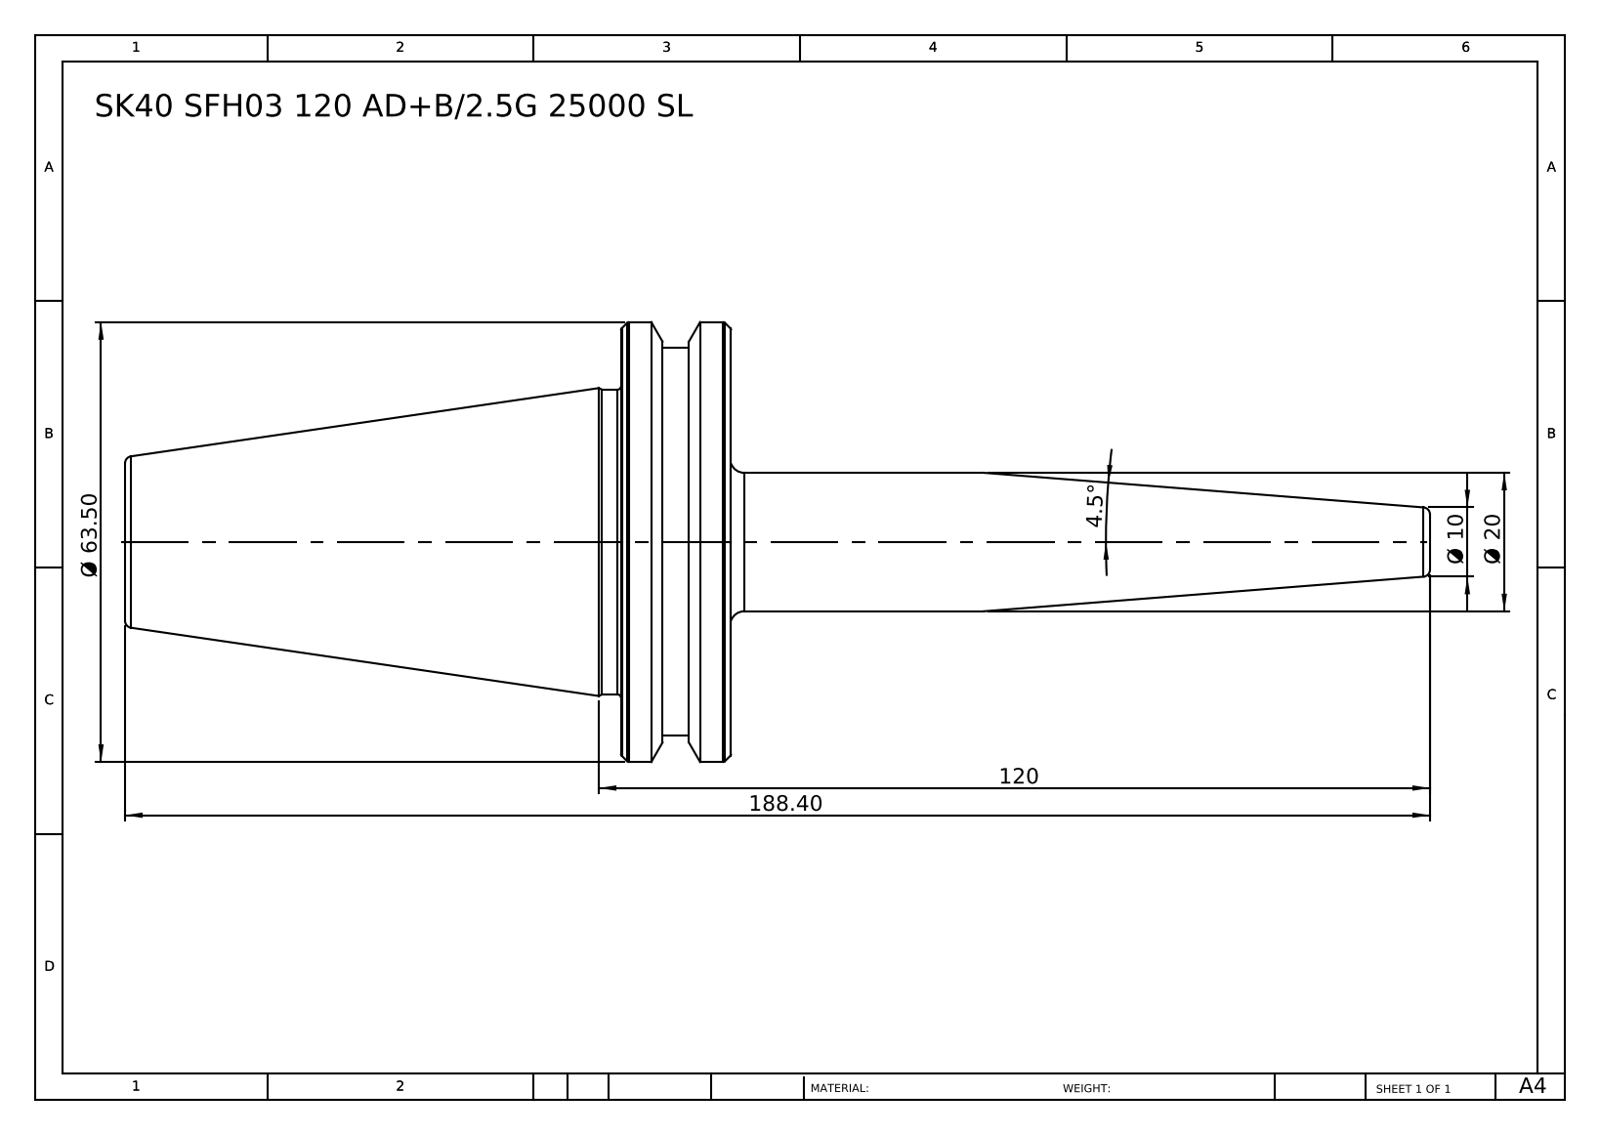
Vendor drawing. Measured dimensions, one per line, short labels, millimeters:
name: SK40 SFH03 120 AD+B-2.5G 25000 SL
written by: SolidWorks 2014 (CONFIG_CONTROL_DESIGN)
unit: mm
bodies: 1 solid, 46 faces (6 planar, 10 cylindrical, 30 other)
size: 188.4 × 63.5 × 63.5
volume: 140 300 mm³; area: 21 953 mm²
bosses: 1× ⌀63.5, 1× ⌀56, 1× ⌀44, 1× ⌀20
face distances: 15.9, 87.5, 71.6, 6.1, 9.8, 81.4, 9.9, 3.8, 6, 77.6
